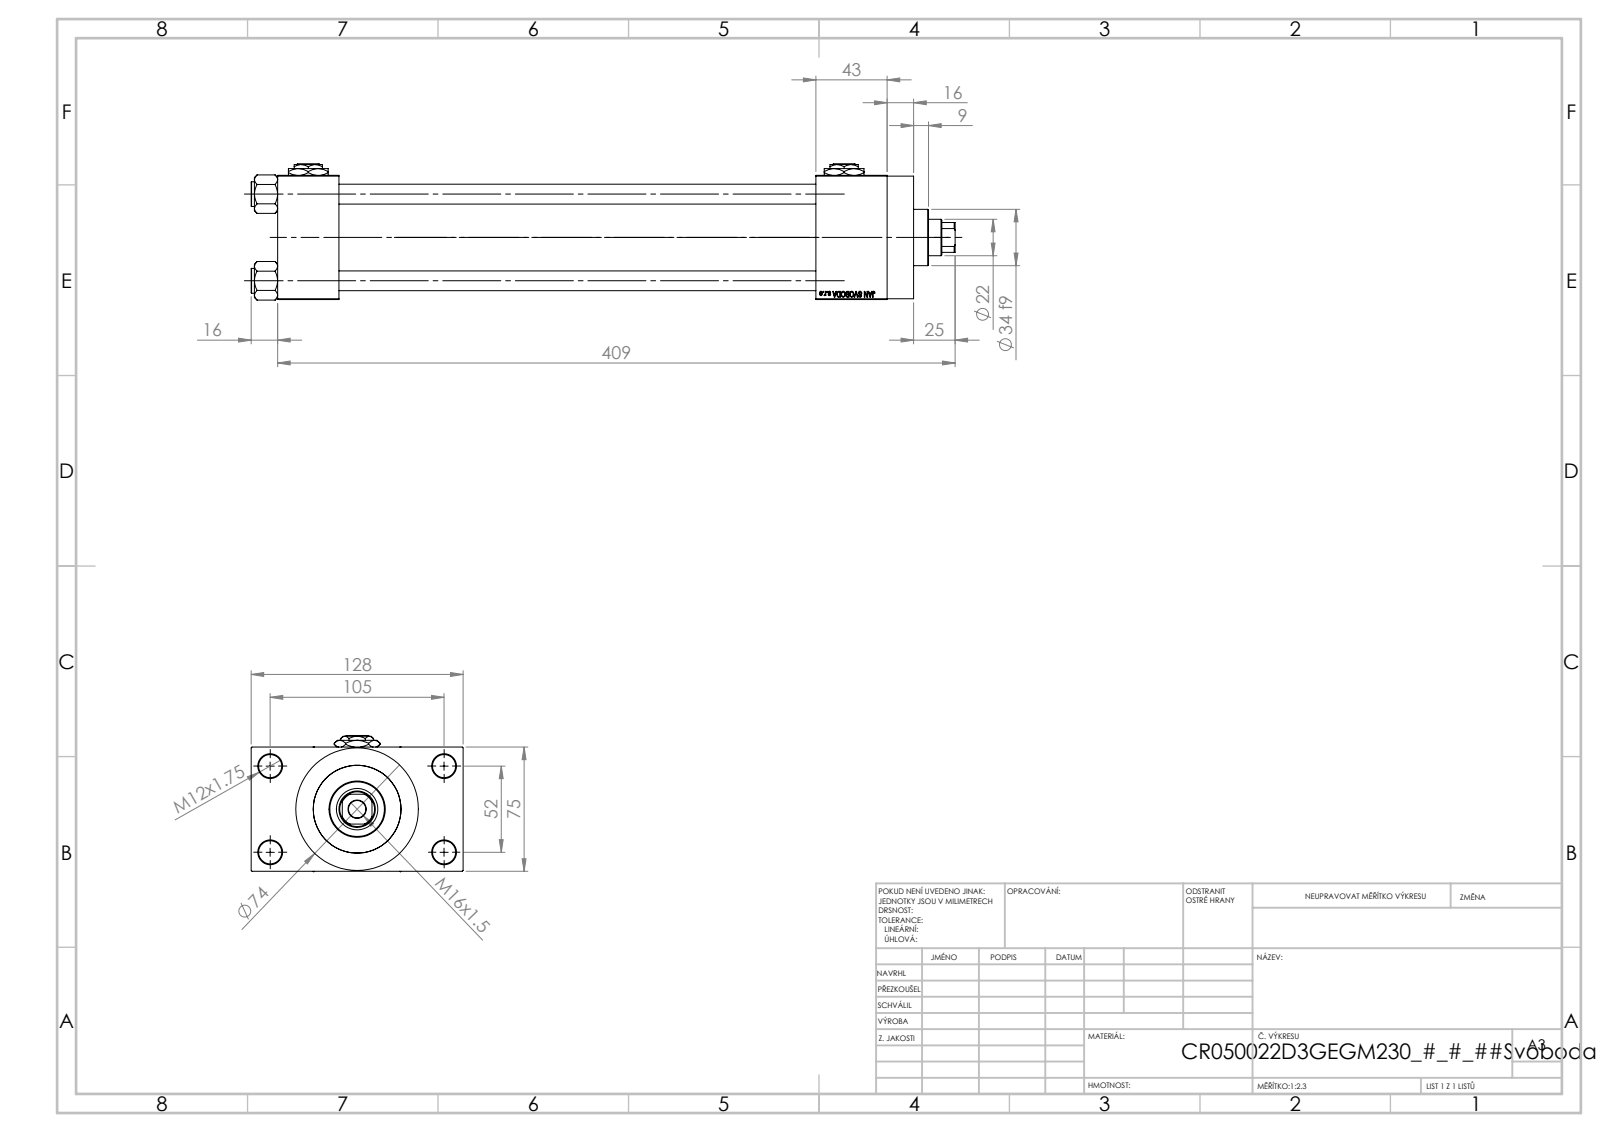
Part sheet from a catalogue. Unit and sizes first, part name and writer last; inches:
Units: inches
Overall size (bounding box): 16.732 × 5.039 × 3.239
Round holes (diameter × count): ⌀0.472 ×4, ⌀0.551 ×4, ⌀0.276 ×2, ⌀0.825 ×2, ⌀1.181 ×2, ⌀0.413 ×1, ⌀0.866 ×1, ⌀0.984 ×1, ⌀1.614 ×1, ⌀1.969 ×1, ⌀2.087 ×1
Round bosses / shafts (diameter × count): ⌀0.591 ×4, ⌀2.913 ×1, ⌀2.205 ×1, ⌀1.339 ×1
Partial cylindrical surfaces — rounded edges, fillets, slot ends (radius × count): R0.413 ×1
Main face-to-face distances: 2.953, 11.339, 1.457, 12.795, 1.043, 3.996, 14.488, 13.031, 1.693, 0.63
Hole centre spacings: 1.037, 1.456, 2.059, 2.3, 2.307, 3.096, 3.715, 2.047
Volume: 67.68 in³ · Surface area: 459.4 in²
Bodies: 13 solids, 1205 faces (545 planar, 100 cylindrical, 560 other)
Part name (STEP PRODUCT): V215CR_D_Body; Zatka_pro_OIL_PORT; NUT_M5_D; V215CR_D_TYCINKA (+2 more)
STEP written by: SolidWorks 2019 (CONFIG_CONTROL_DESIGN)
